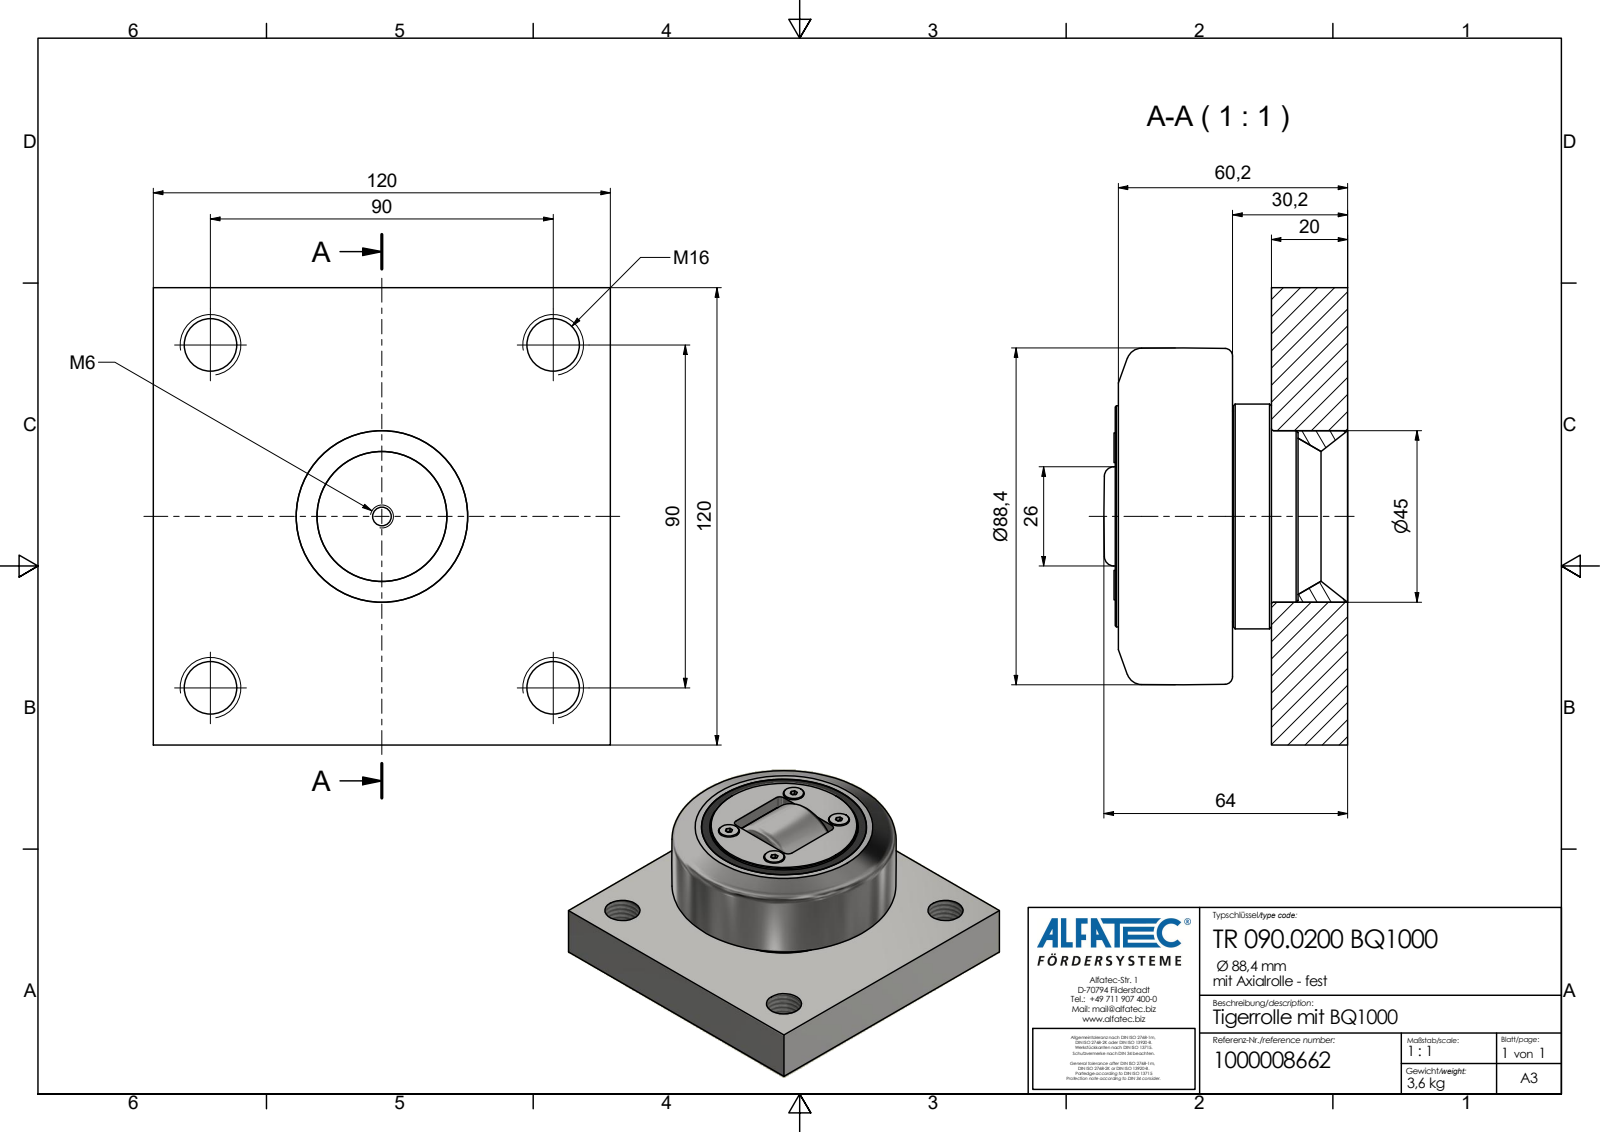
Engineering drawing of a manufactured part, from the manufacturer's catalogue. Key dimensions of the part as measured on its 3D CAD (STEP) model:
Part name (STEP PRODUCT): TR 090.0200 BQ1000_Kontur
STEP written by: Autodesk Inventor 2020 (AP242_MANAGED_MODEL_BASED_3D_ENGINEERING_MIM_LF)
Units: millimetres
Bodies: 1 solid, 86 faces (52 planar, 19 cylindrical, 15 other)
Overall size (bounding box): 120 × 120 × 64
Volume: 476 881 mm³ · Surface area: 58 380 mm²
Round holes (diameter × count): ⌀13.84 ×4, ⌀2.5 ×1, ⌀4.92 ×1
Round bosses / shafts (diameter × count): ⌀7.8 ×4, ⌀59 ×1, ⌀58 ×1, ⌀55.3 ×1
Partial cylindrical surfaces — rounded edges, fillets, slot ends (radius × count): R2 ×4, R1.5 ×1, R25 ×1
Main face-to-face distances: 20, 120, 30.2, 10.2, 30, 61, 41, 30.8, 60.2, 40.2
Hole centre spacings: 63.64, 90, 127.28
